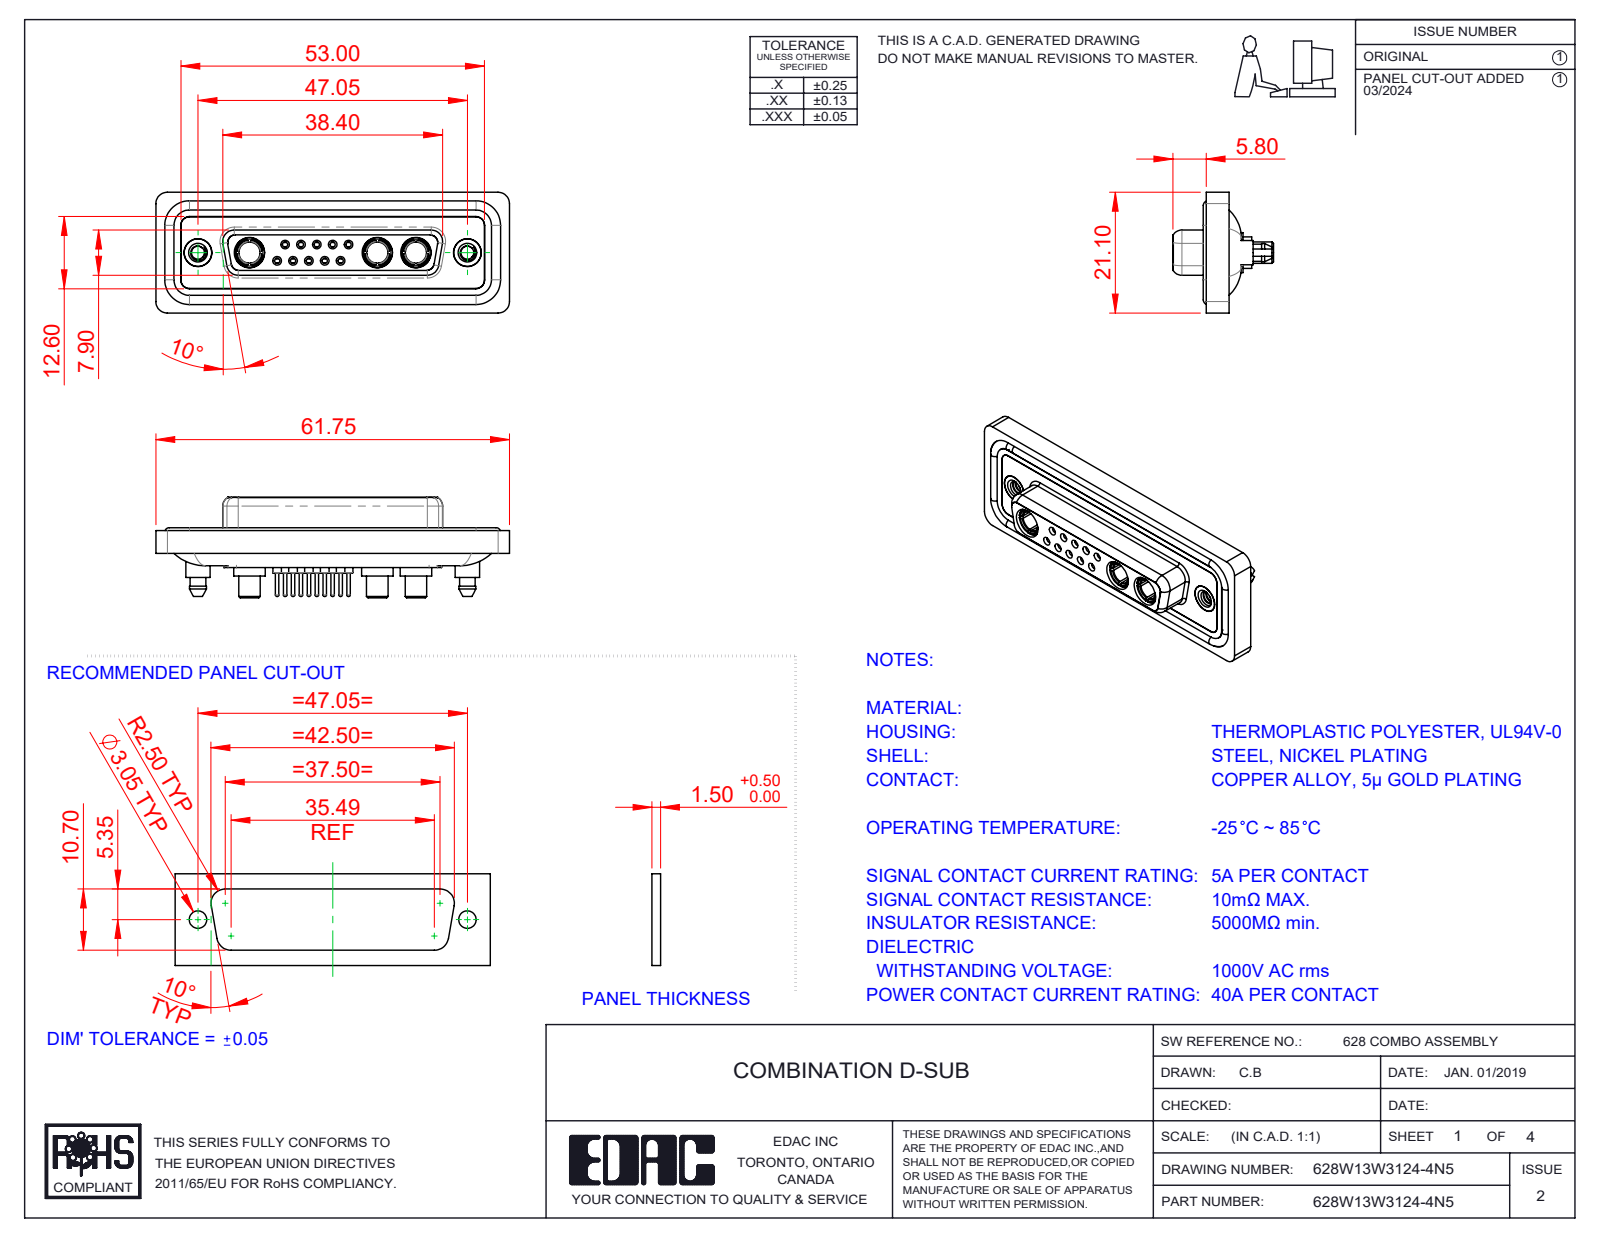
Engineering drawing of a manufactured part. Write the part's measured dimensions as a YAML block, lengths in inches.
part_name: "628Combo Shell Rear_25 Contacts; 628Combo Shell Front_25 Contacts; 628Combo Threaded Boardlock_5; 628Combo Waterproof Housing_25 Contacts (+5 more)"
step_written_by: "SolidWorks 2023 (CONFIG_CONTROL_DESIGN)"
units: inches
bodies: {solids: 23, faces: 1208, planar: 358, cylindrical: 479, other: 371}
overall_size: [2.431, 0.831, 0.691]
volume: 0.516
surface_area: 21.81
round_holes:
  - {diameter: 0.035, count: 10}
  - {diameter: 0.043, count: 10}
  - {diameter: 0.059, count: 10}
  - {diameter: 0.079, count: 10}
  - {diameter: 0.063, count: 5}
  - {diameter: 0.067, count: 5}
  - {diameter: 0.191, count: 5}
  - {diameter: 0.146, count: 3}
  - {diameter: 0.209, count: 3}
  - {diameter: 0.089, count: 2}
  - {diameter: 0.157, count: 2}
  - {diameter: 0.159, count: 2}
round_bosses_or_shafts:
  - {diameter: 0.087, count: 10}
  - {diameter: 0.024, count: 10}
  - {diameter: 0.063, count: 9}
  - {diameter: 0.217, count: 3}
  - {diameter: 0.205, count: 3}
  - {diameter: 0.195, count: 3}
  - {diameter: 0.187, count: 3}
  - {diameter: 0.148, count: 3}
partial_cylinders:
  - {radius: 0.059, count: 24}
  - {radius: 0.079, count: 18}
  - {radius: 0.063, count: 10}
  - {radius: 0.053, count: 8}
  - {radius: 0.01, count: 4}
  - {radius: 0.02, count: 4}
  - {radius: 0.024, count: 4}
  - {radius: 0.026, count: 4}
face_to_face_distances: [0.016, 0.071, 0.293, 0.222, 0.02, 0.26, 0.278, 0.063, 0.114, 0.043]
hole_center_spacings: [0.124, 0.109, 0.198, 0.198, 0.218, 0.327, 0.295, 0.109]
